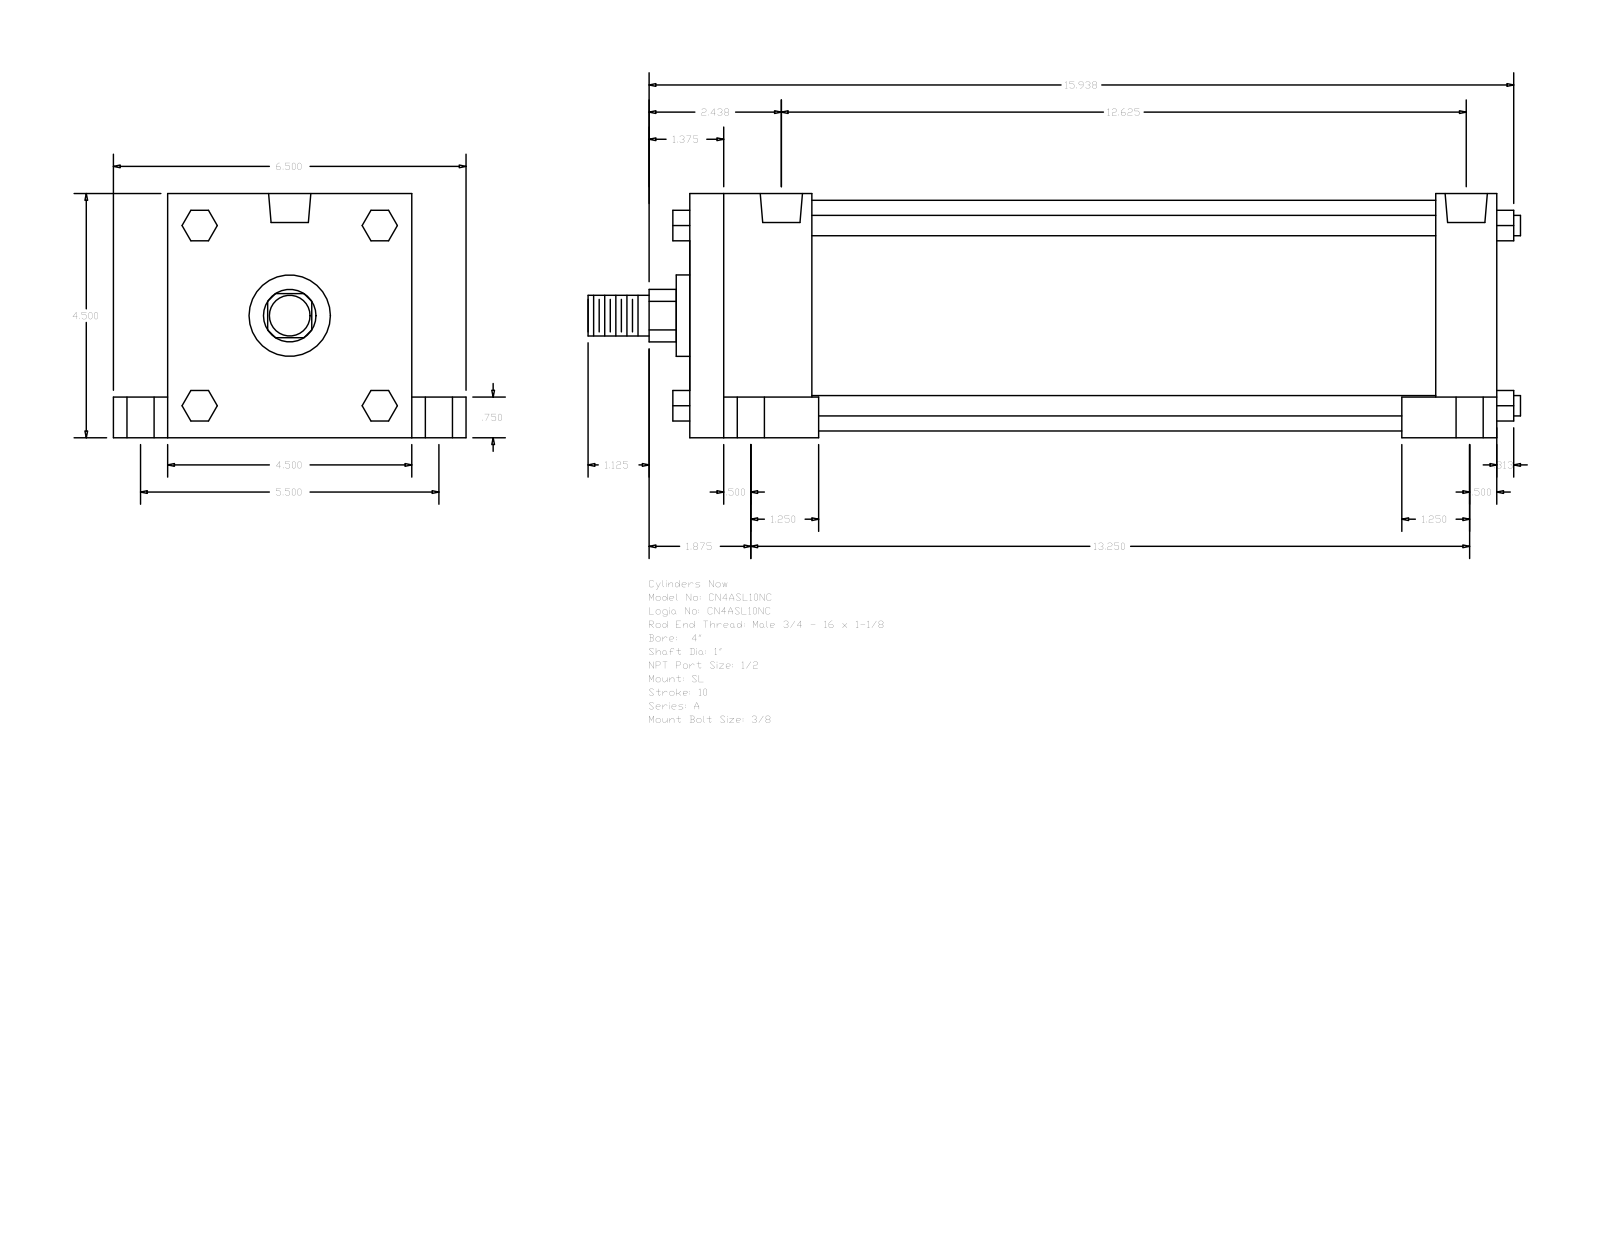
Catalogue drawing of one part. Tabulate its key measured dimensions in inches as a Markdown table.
| quantity | value |
| --- | --- |
| part name | A_SL__0400_1 |
| STEP written by | GSSL Pune (CONFIG_CONTROL_DESIGN) |
| units | inches |
| bodies | 0 solids, 150 faces (114 planar, 36 cylindrical, 0 other) |
| overall size | 17.187 × 6.5 × 4.5 |
| round holes (diameter × count) | 0.344 × 4, 0.5 × 4, 0.75 × 4, 0.778 × 2 |
| round bosses / shafts (diameter × count) | 0.375 × 4, 4.25 × 1, 1.5 × 1, 1 × 1, 0.75 × 1 |
| partial cylindrical surfaces (radius × count) | 0.484 × 1 |
| main face-to-face distances | 4.5, 14.875, 2.25, 12.625, 13.75, 11.5, 1.125, 0.75, 1, 5.5 |
| hole center spacings | 0.125, 2.751, 2.756, 2.807, 2.835, 5.5, 12.375, 12.5 |
